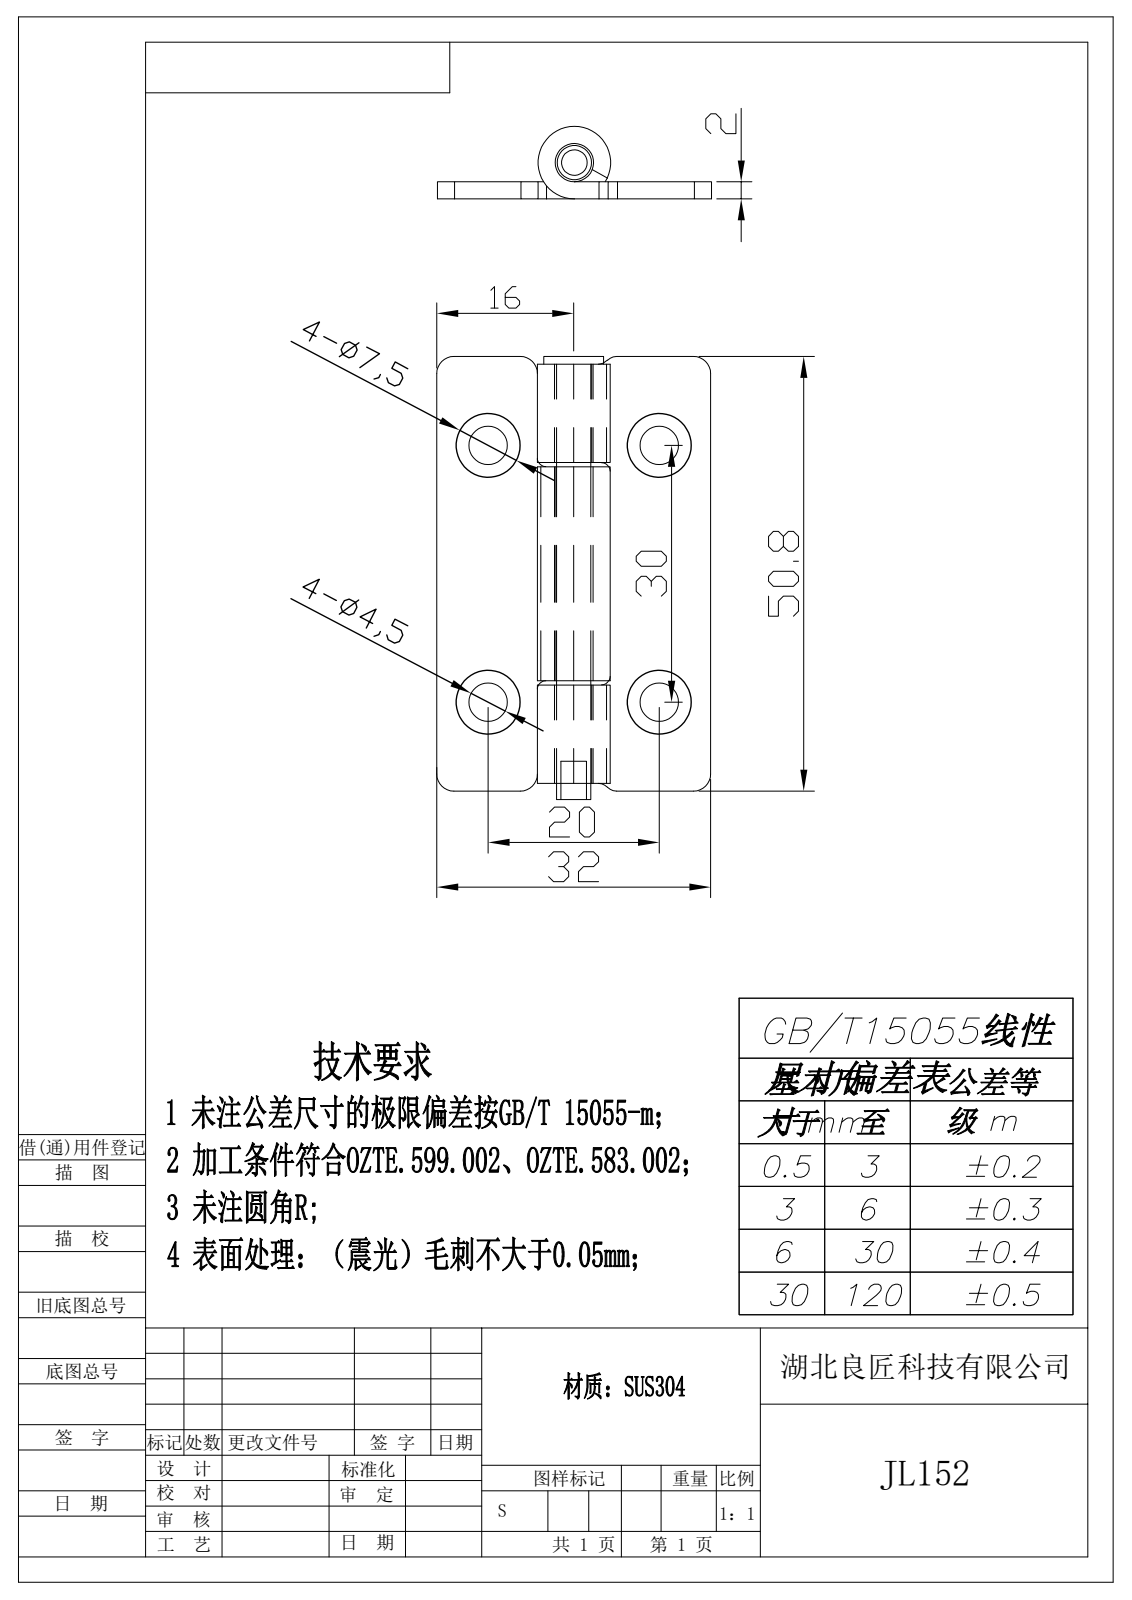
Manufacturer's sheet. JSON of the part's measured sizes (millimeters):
{"step_written_by": "Rhino 8.5 (CONFIG_CONTROL_DESIGN)", "units": "millimeters", "bodies": {"solids": 3, "faces": 70, "planar": 26, "cylindrical": 32, "other": 12}, "overall_size": [52, 32, 8.5], "volume_mm3": 4837, "surface_area_mm2": 5837, "round_holes": [[4.5, 5], [3, 1]], "round_bosses_or_shafts": [[8.5, 1], [4, 1]], "partial_cylinders_radius": [[2, 6], [1, 4], [1.5, 4]], "face_to_face_distances": [2, 32, 11.75, 20.25, 0.5, 25.5, 12, 37, 11.5, 37.5], "hole_center_spacings": [20, 30, 36.06]}
